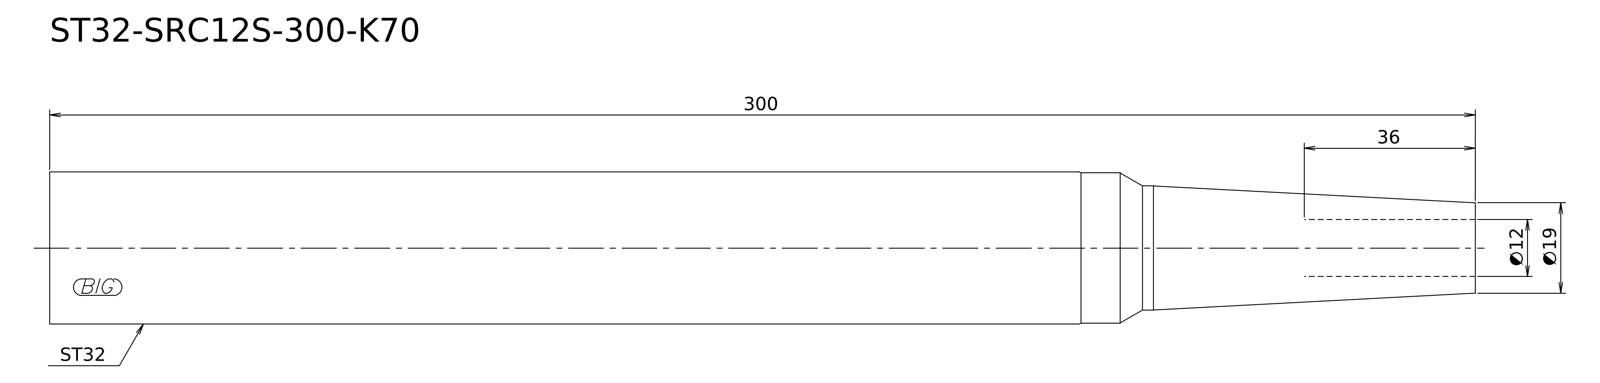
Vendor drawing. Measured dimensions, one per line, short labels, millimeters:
written by: Kubotek KeyCreator V8.5.1 (14335) (CONFIG_CONTROL_DESIGN)
unit: mm
bodies: 1 solid, 8 faces (2 planar, 3 cylindrical, 3 other)
size: 300 × 32 × 32
volume: 212 588 mm³; area: 29 215 mm²
bosses: 1× ⌀32, 1× ⌀31.6, 1× ⌀26.1
face distances: 300
